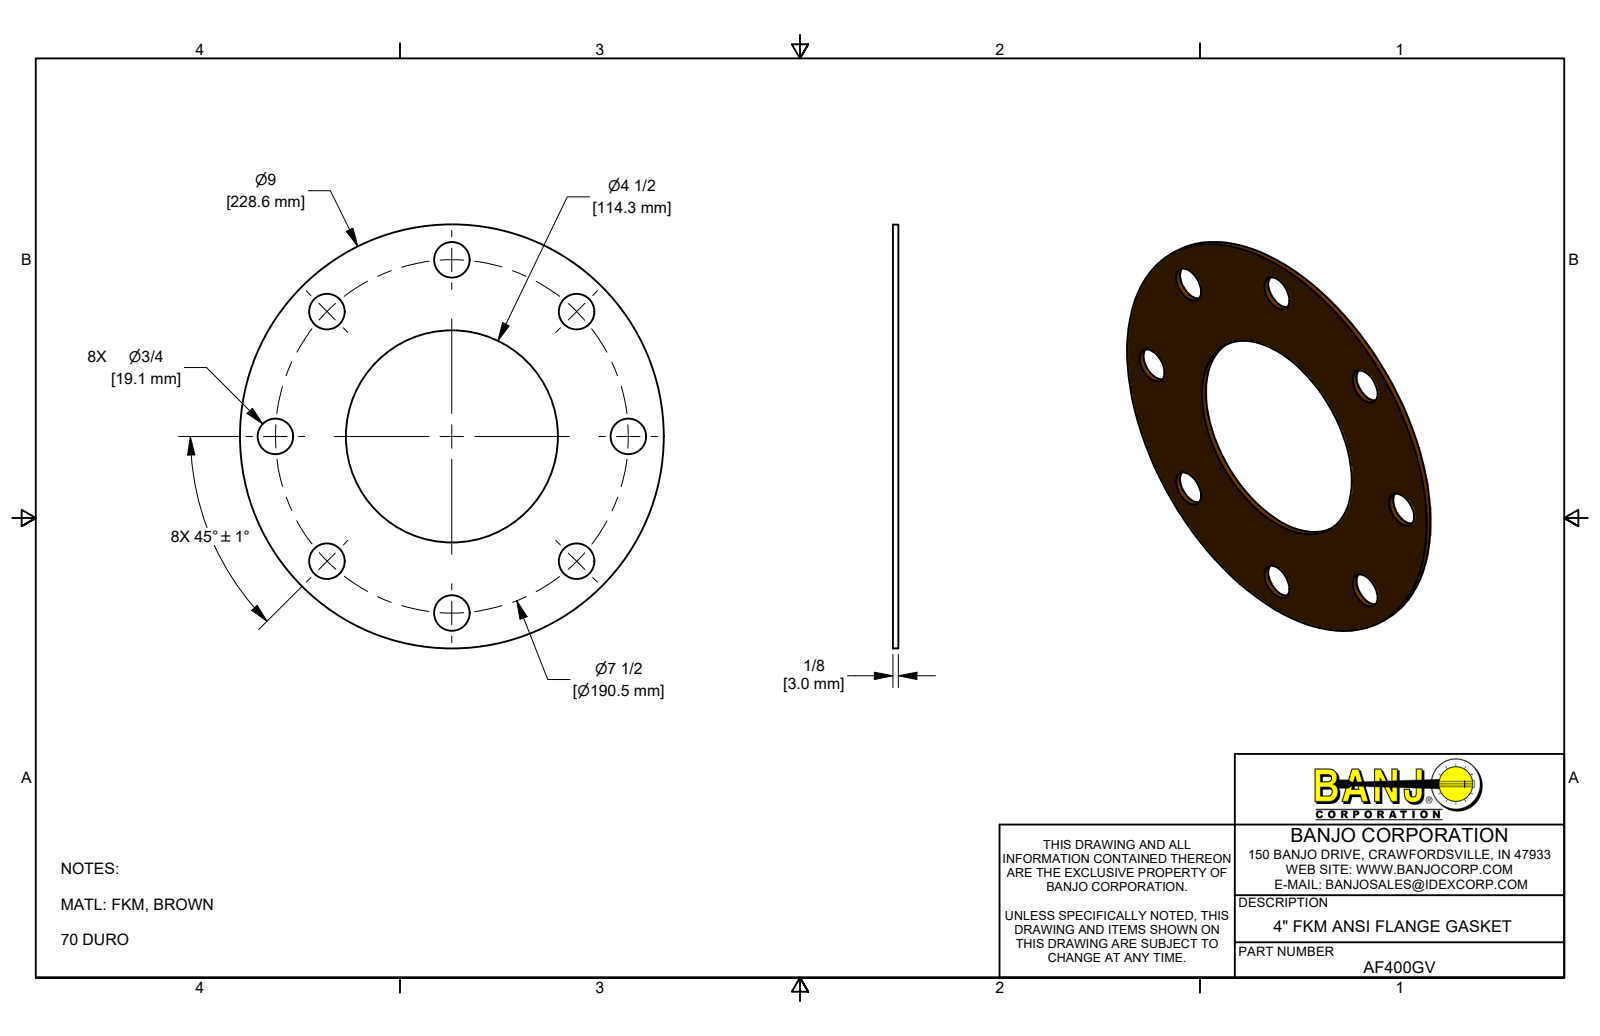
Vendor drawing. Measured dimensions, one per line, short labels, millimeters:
name: AF400GV
written by: Autodesk Inventor 2019 (AUTOMOTIVE_DESIGN)
unit: mm
bodies: 1 solid, 12 faces (2 planar, 10 cylindrical, 0 other)
size: 228.6 × 228.6 × 3
volume: 85 430 mm³; area: 61 670 mm²
holes: 8× ⌀19.1, 1× ⌀114.3
bosses: 1× ⌀228.6
face distances: 3
hole spacings: 72.9, 95.3, 134.7, 176, 190.5, 190.5
